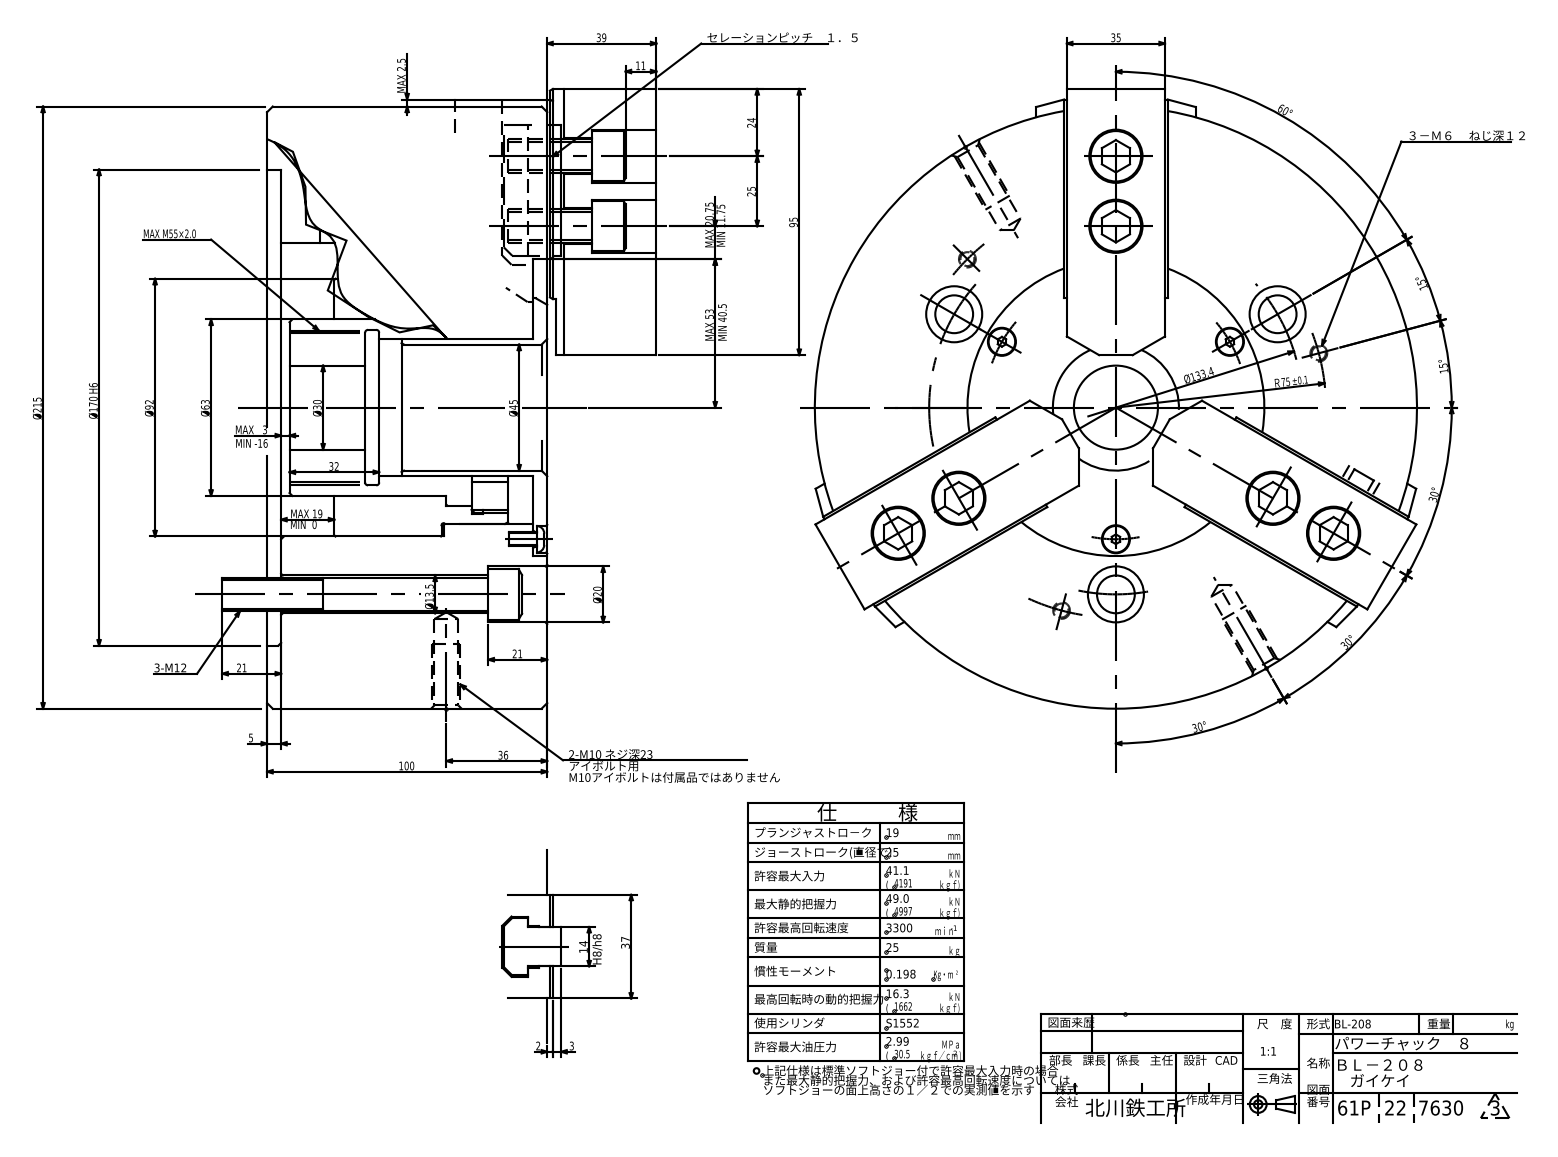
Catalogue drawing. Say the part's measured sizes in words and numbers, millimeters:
The part is named "BL208-Solid". Its 3-D file was written by "ST-DEVELOPER v16.7 (AUTOMOTIVE_DESIGN)". It is 1 solid with 2936 faces: 2117 planar, 658 cylindrical and 161 other. Overall it measures 215 by 215 by 155.2 millimeters. Its volume is 3 551 000 cubic millimeters and its surface area 313 498 square millimeters. Round holes: 6 of diameter 10.3, 6 of diameter 13, 6 of diameter 19, 3 of diameter 4.2, 3 of diameter 5.2, 3 of diameter 5.5, 3 of diameter 10, 3 of diameter 13.5, 3 of diameter 20, 1 of diameter 8.5, 1 of diameter 30, 1 of diameter 45. Round bosses or shafts: 9 of diameter 18, 9 of diameter 11.7, 3 of diameter 9.5, 3 of diameter 4.83, 1 of diameter 215, 1 of diameter 83, 1 of diameter 75. Partial cylindrical surfaces (rounded edges, fillets, slot ends): 117 of radius 0.1, 9 of radius 0.8, 3 of radius 7.5, 3 of radius 10.75, 2 of radius 5, 1 of radius 0.51, 1 of radius 2.19, 1 of radius 4.08. The main face-to-face distances are 95, 5, 100, 39.2, 35, 139.2, 134.2, 11, 9.5, 33. The hole center spacings are 53.68, 63, 72.5, 76.49, 98.96, 123.61, 19.7, 20.24.
